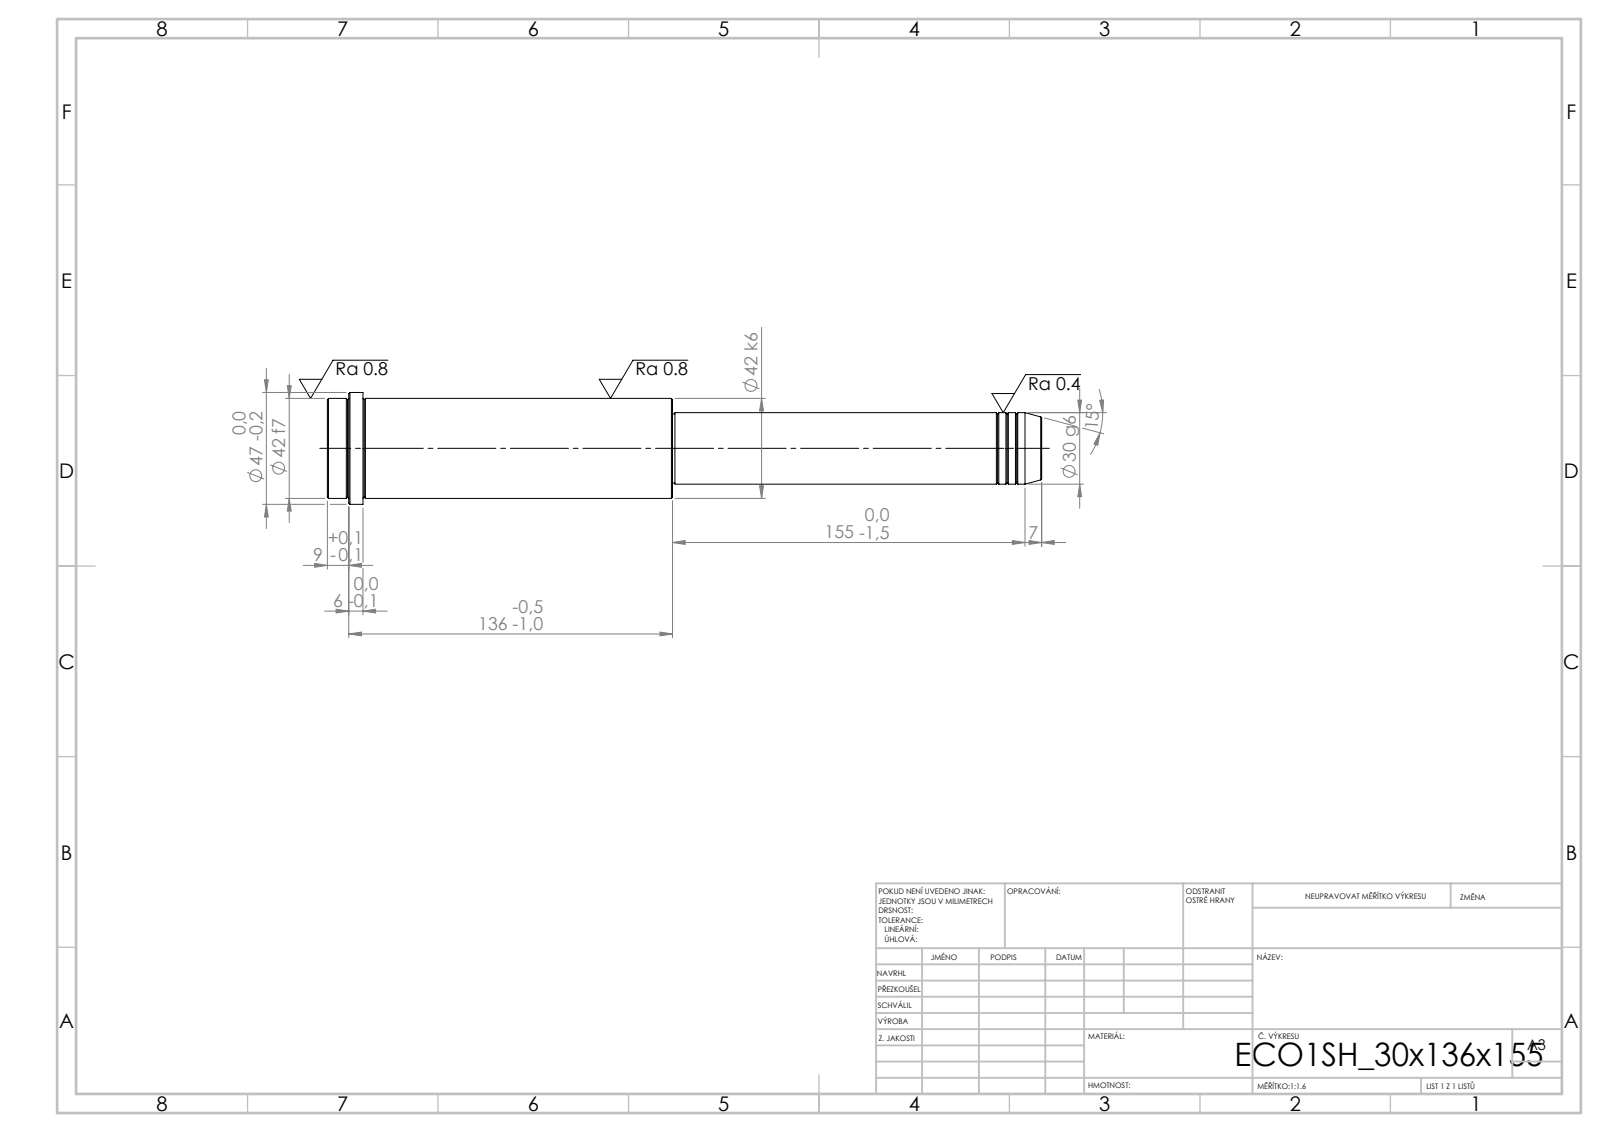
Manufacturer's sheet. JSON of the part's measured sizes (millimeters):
{"step_written_by": "SolidWorks 2019 (CONFIG_CONTROL_DESIGN)", "units": "millimeters", "bodies": {"solids": 1, "faces": 52, "planar": 6, "cylindrical": 16, "other": 30}, "overall_size": [300, 47, 47], "volume_mm3": 311645, "surface_area_mm2": 37375, "round_bosses_or_shafts": [[47, 1], [42, 1], [30, 1], [29, 1]], "face_to_face_distances": [145, 155, 300, 285, 130, 15, 291, 136, 6, 9]}
